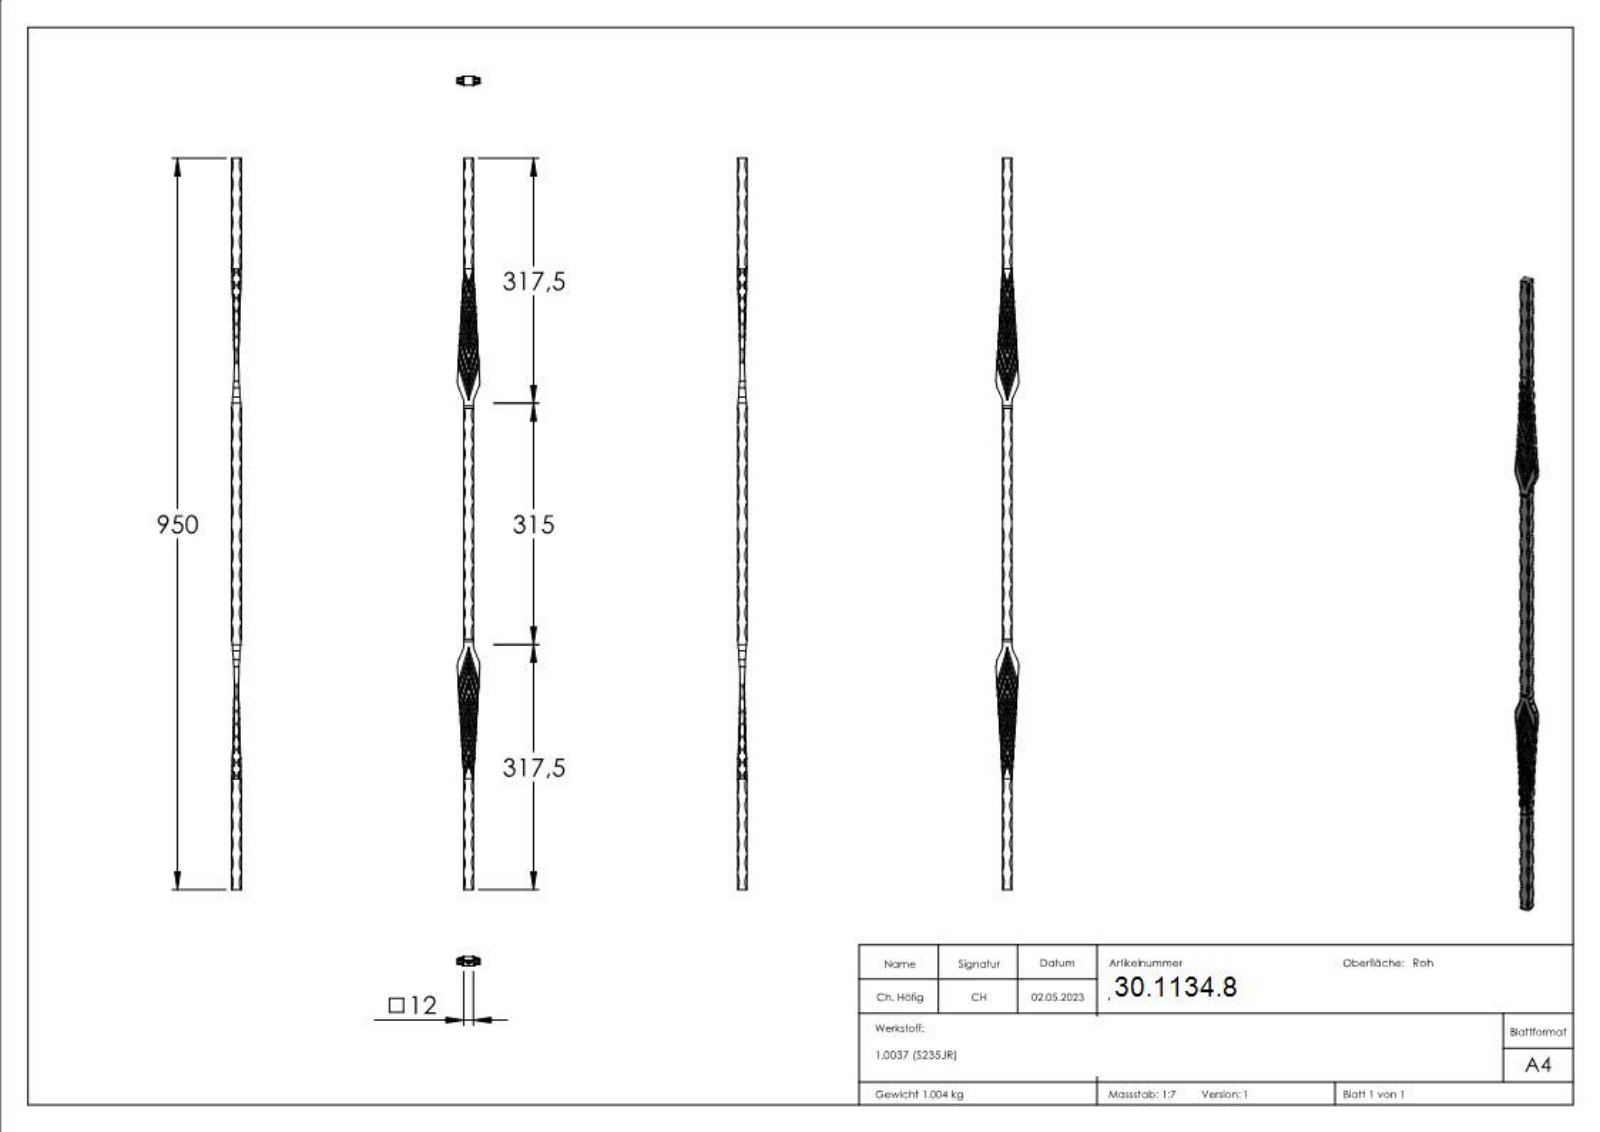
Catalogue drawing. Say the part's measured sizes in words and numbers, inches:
The part is named "578-3". Its 3-D file was written by "SolidWorks 2018 (CONFIG_CONTROL_DESIGN)". It is 1 solid with 944 faces: 405 planar, 220 cylindrical and 319 other. Overall it measures 37.402 by 1.161 by 0.472 inches. Its volume is 7.857 cubic inches and its surface area 81.64 square inches. Partial cylindrical surfaces (rounded edges, fillets, slot ends): 88 of radius 0.039, 80 of radius 0.008, 8 of radius 0.787, 4 of radius 1.181, 4 of radius 23.699. The main face-to-face distances are 0.472, 0.16, 0.083, 0.32, 3.128, 0.076, 3.287, 0.243, 2.968, 2.037.
